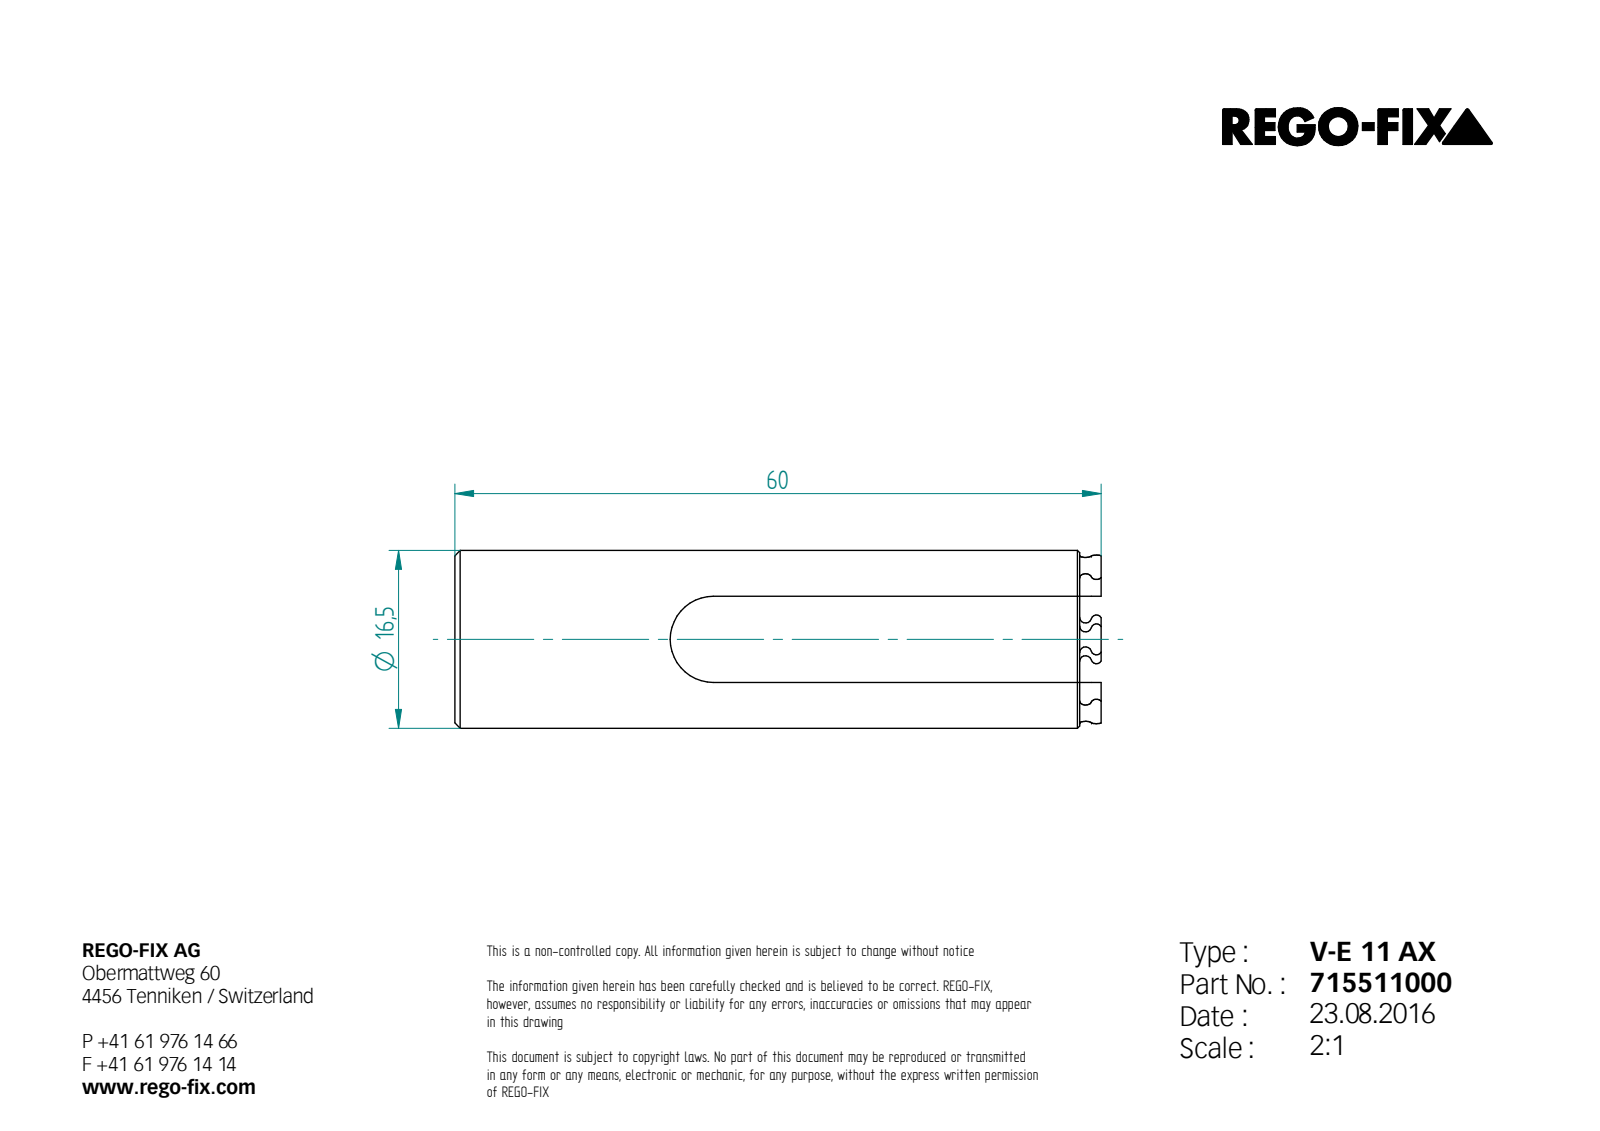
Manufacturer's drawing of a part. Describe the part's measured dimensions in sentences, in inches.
Its 3-D file was written by "Unknown (AUTOMOTIVE_DESIGN)". It is 1 solid with 60 faces: 22 planar, 17 cylindrical and 21 other. Overall it measures 2.362 by 0.65 by 0.65 inches. Its volume is 0.477 cubic inches and its surface area 7.282 square inches. Round holes: 1 of diameter 0.354. Round bosses or shafts: 1 of diameter 0.65. Partial cylindrical surfaces (rounded edges, fillets, slot ends): 1 of radius 0.14, 1 of radius 0.157, 1 of radius 0.185, 1 of radius 0.317. The main face-to-face distances are 0.315, 0.258, 2.283, 0.286, 0.029, 0.028, 0.287, 2.362, 0.079, 0.346.
